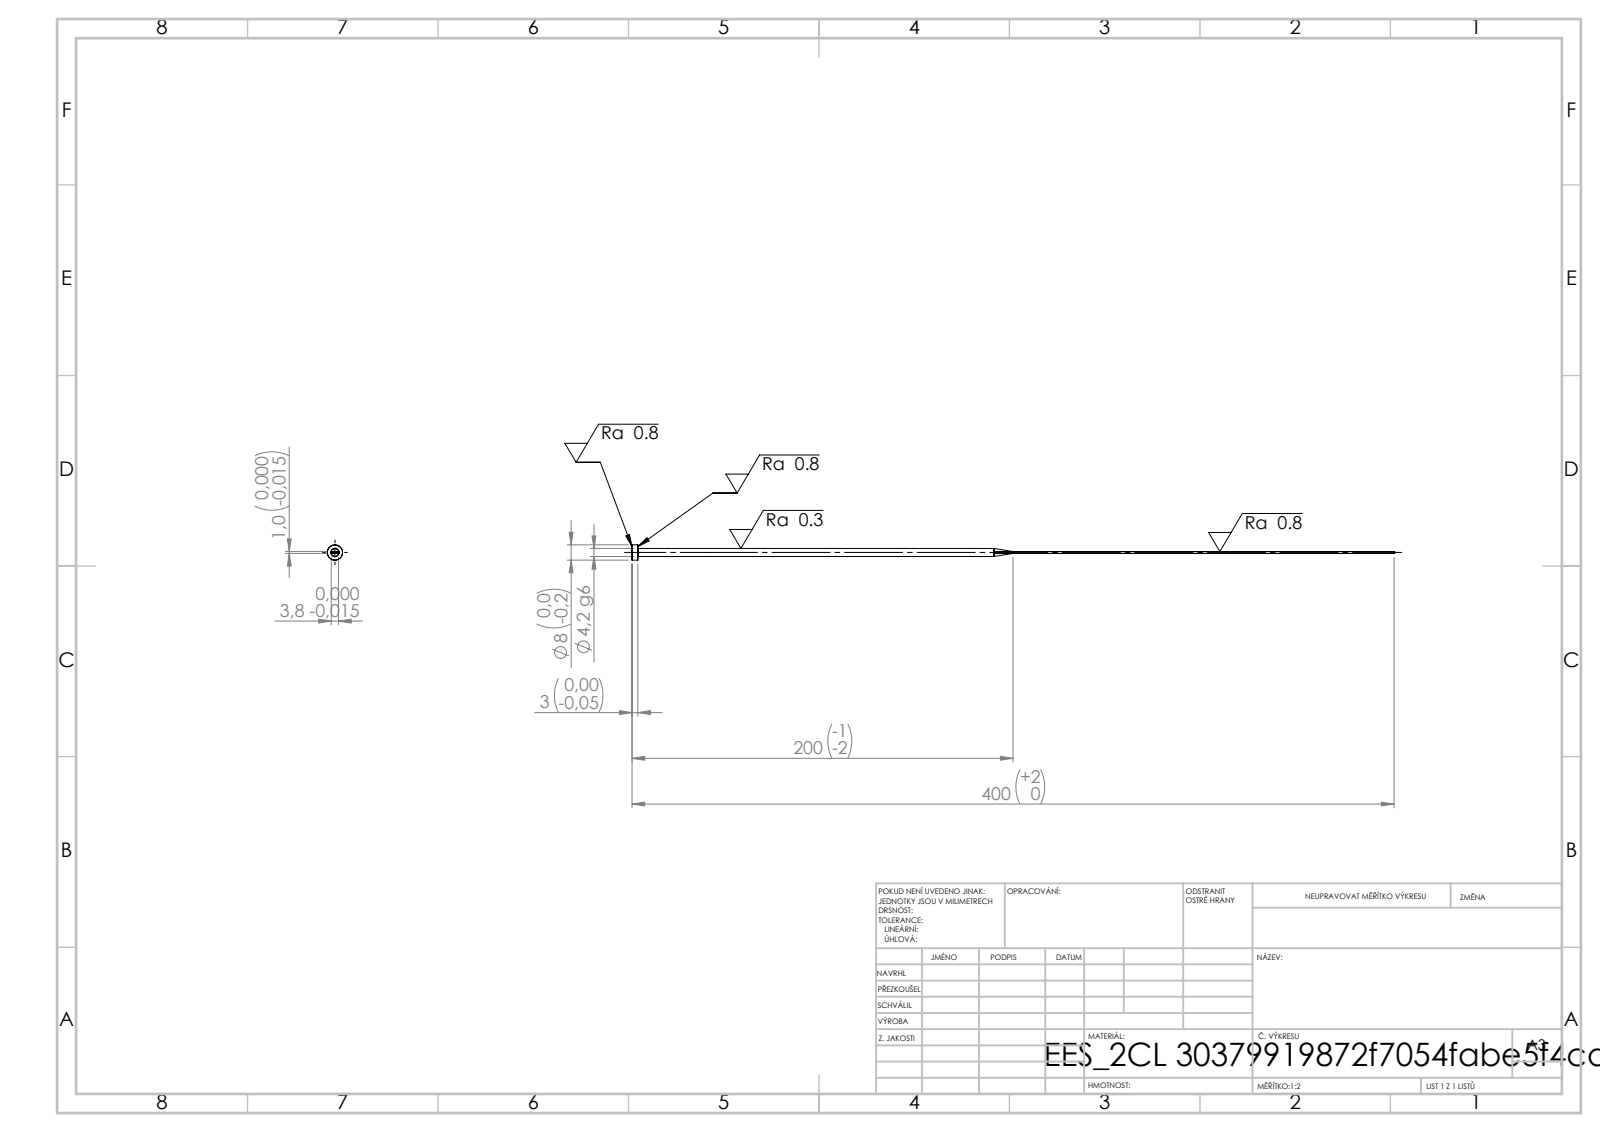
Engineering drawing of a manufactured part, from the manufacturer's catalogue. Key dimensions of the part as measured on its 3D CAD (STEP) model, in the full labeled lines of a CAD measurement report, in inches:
STEP written by: SolidWorks 2019 (CONFIG_CONTROL_DESIGN)
Units: inches
Bodies: 1 solid, 15 faces (7 planar, 4 cylindrical, 4 other)
Overall size (bounding box): 15.748 × 0.315 × 0.315
Volume: 0.219 in³ · Surface area: 7.228 in²
Round bosses / shafts (diameter × count): ⌀0.315 ×1, ⌀0.165 ×1
Main face-to-face distances: 0.039, 0.15, 0.118, 15.748, 15.63
